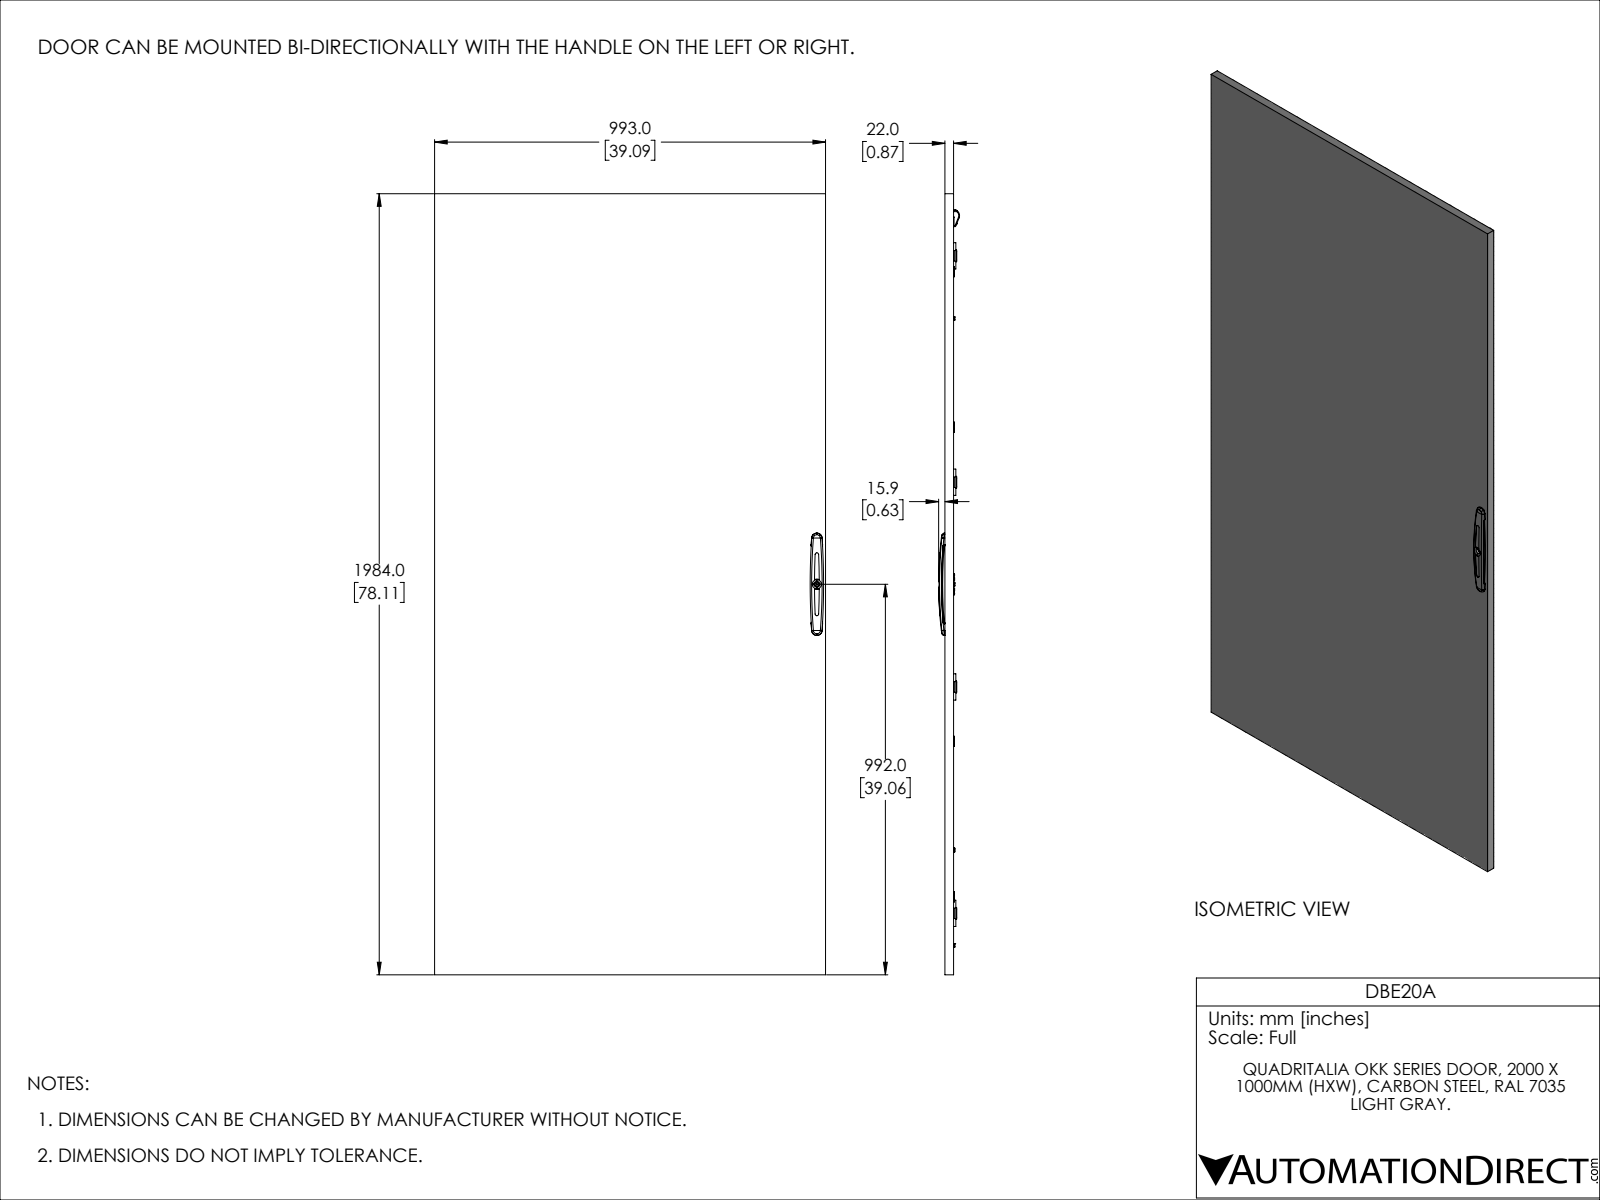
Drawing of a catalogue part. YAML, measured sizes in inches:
part_name: "DBE20A"
step_written_by: "SolidWorks 2021 (CONFIG_CONTROL_DESIGN)"
units: inches
bodies: {solids: 88, faces: 3336, planar: 1600, cylindrical: 1203, other: 533}
overall_size: [78.11, 39.094, 2.091]
volume: 337.7
surface_area: 8411
round_holes:
  - {diameter: 0.167, count: 160}
  - {diameter: 0.354, count: 20}
  - {diameter: 0.01, count: 8}
  - {diameter: 0.197, count: 8}
  - {diameter: 0.194, count: 6}
  - {diameter: 0.194, count: 4}
  - {diameter: 0.244, count: 4}
  - {diameter: 0.276, count: 4}
  - {diameter: 0.205, count: 3}
  - {diameter: 0.134, count: 2}
  - {diameter: 0.169, count: 2}
  - {diameter: 0.173, count: 2}
round_bosses_or_shafts:
  - {diameter: 0.276, count: 23}
  - {diameter: 0.236, count: 19}
  - {diameter: 0.283, count: 10}
  - {diameter: 0.193, count: 8}
  - {diameter: 0.472, count: 2}
  - {diameter: 0.394, count: 2}
  - {diameter: 0.315, count: 2}
  - {diameter: 0.157, count: 2}
partial_cylinders:
  - {radius: 0.012, count: 74}
  - {radius: 0.039, count: 70}
  - {radius: 0.02, count: 41}
  - {radius: 0.059, count: 36}
  - {radius: 0.098, count: 28}
  - {radius: 0.079, count: 19}
  - {radius: 0.177, count: 16}
  - {radius: 0.008, count: 10}
face_to_face_distances: [0.079, 0.059, 0.728, 0.787, 0.669, 33.858, 0.866, 0.138, 0.807, 39.016]
hole_center_spacings: [0.984, 1.969, 2.953, 3.937, 4.921, 5.906, 6.89, 8.858]
